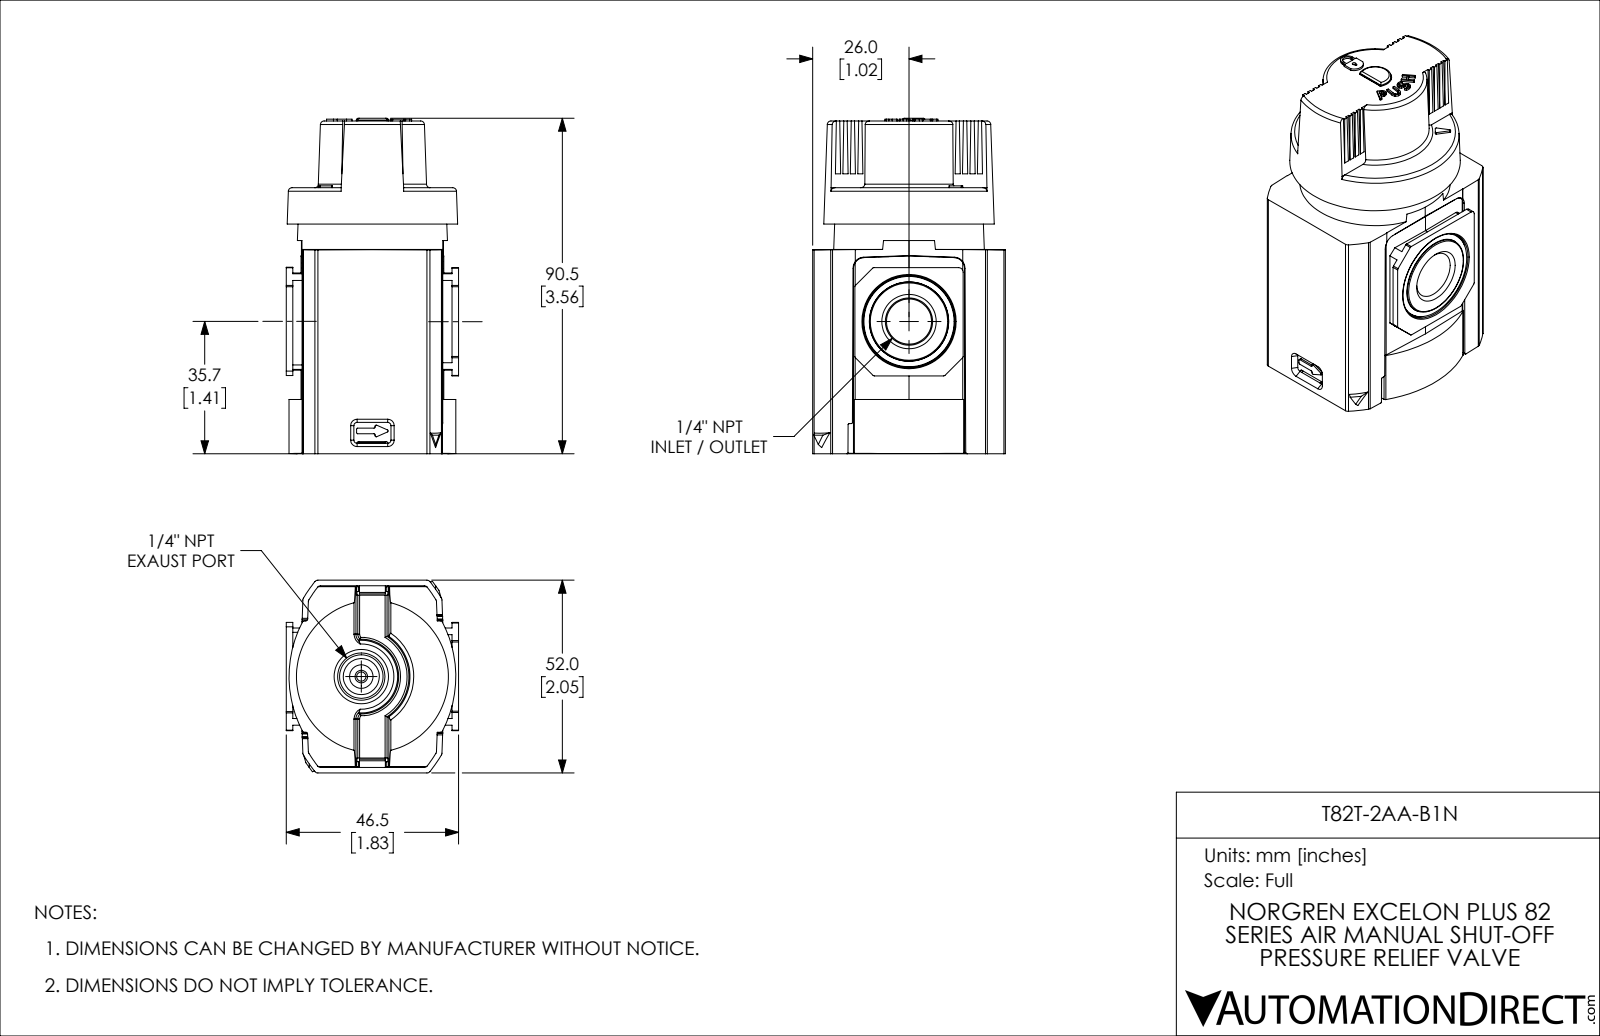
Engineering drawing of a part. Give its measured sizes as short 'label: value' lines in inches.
name: T82T-2AA-B1N
written by: SolidWorks 2021 (CONFIG_CONTROL_DESIGN)
unit: in
bodies: 3 solids, 804 faces (382 planar, 245 cylindrical, 177 other)
size: 3.563 × 2.047 × 1.831
volume: 5.938 in³; area: 71.23 in²
holes: 1× ⌀0.039, 1× ⌀0.199
bosses: 1× ⌀1.173, 1× ⌀0.807, 1× ⌀0.78, 1× ⌀0.768, 1× ⌀0.236
rounds: 41× R0.02, 34× R0.039, 13× R0.01, 8× R0.118, 7× R0.012, 4× R0.047, 2× R0.004, 2× R0.016
face distances: 0.059, 1.988, 2.047, 1.929, 1.169, 0.182, 1.352, 0.123, 1.293, 1.475
